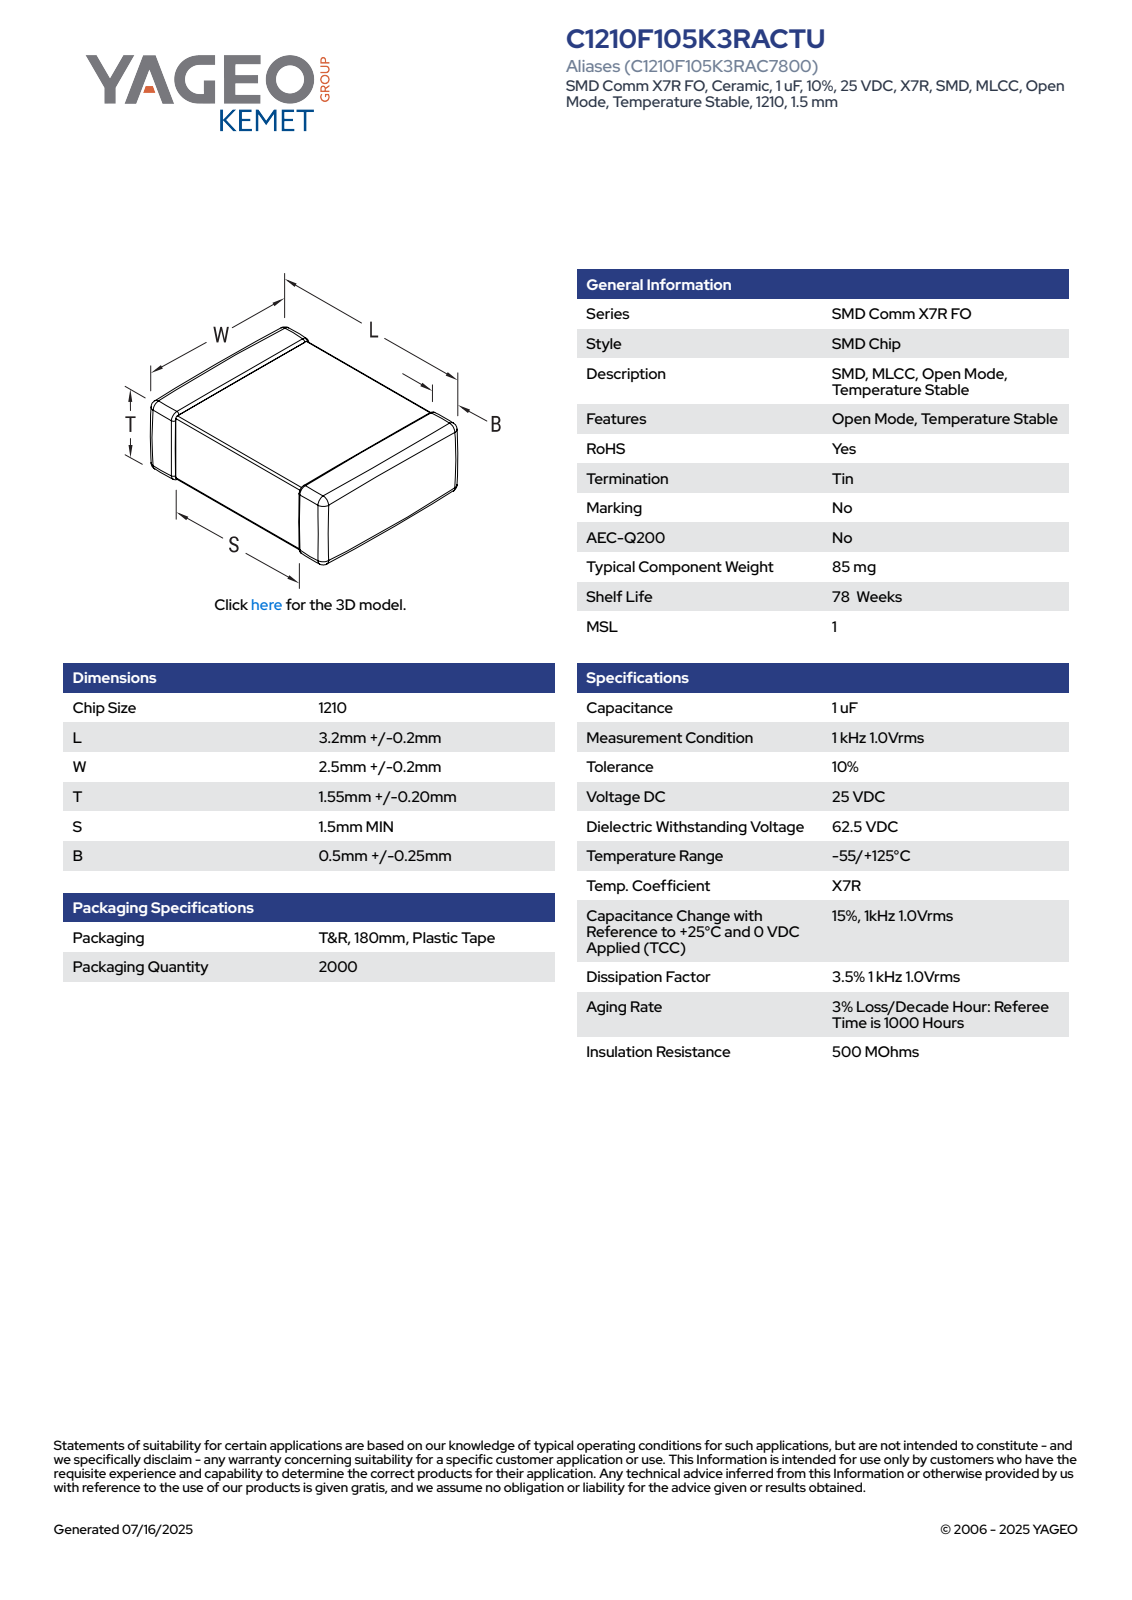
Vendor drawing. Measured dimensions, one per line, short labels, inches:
name: CCS_CCSTDNOS_1210_L3.4W2.7T1.75B0.75
written by: SolidWorks 2014 (AUTOMOTIVE_DESIGN)
unit: in
bodies: 4 solids, 125 faces (71 planar, 38 cylindrical, 16 other)
size: 0.134 × 0.106 × 0.069
volume: 0.001 in³; area: 0.06 in²
face distances: 0.067, 0.064, 0.134, 0.104, 0.069, 0.102, 0.106, 0.067, 0.065, 0.052
